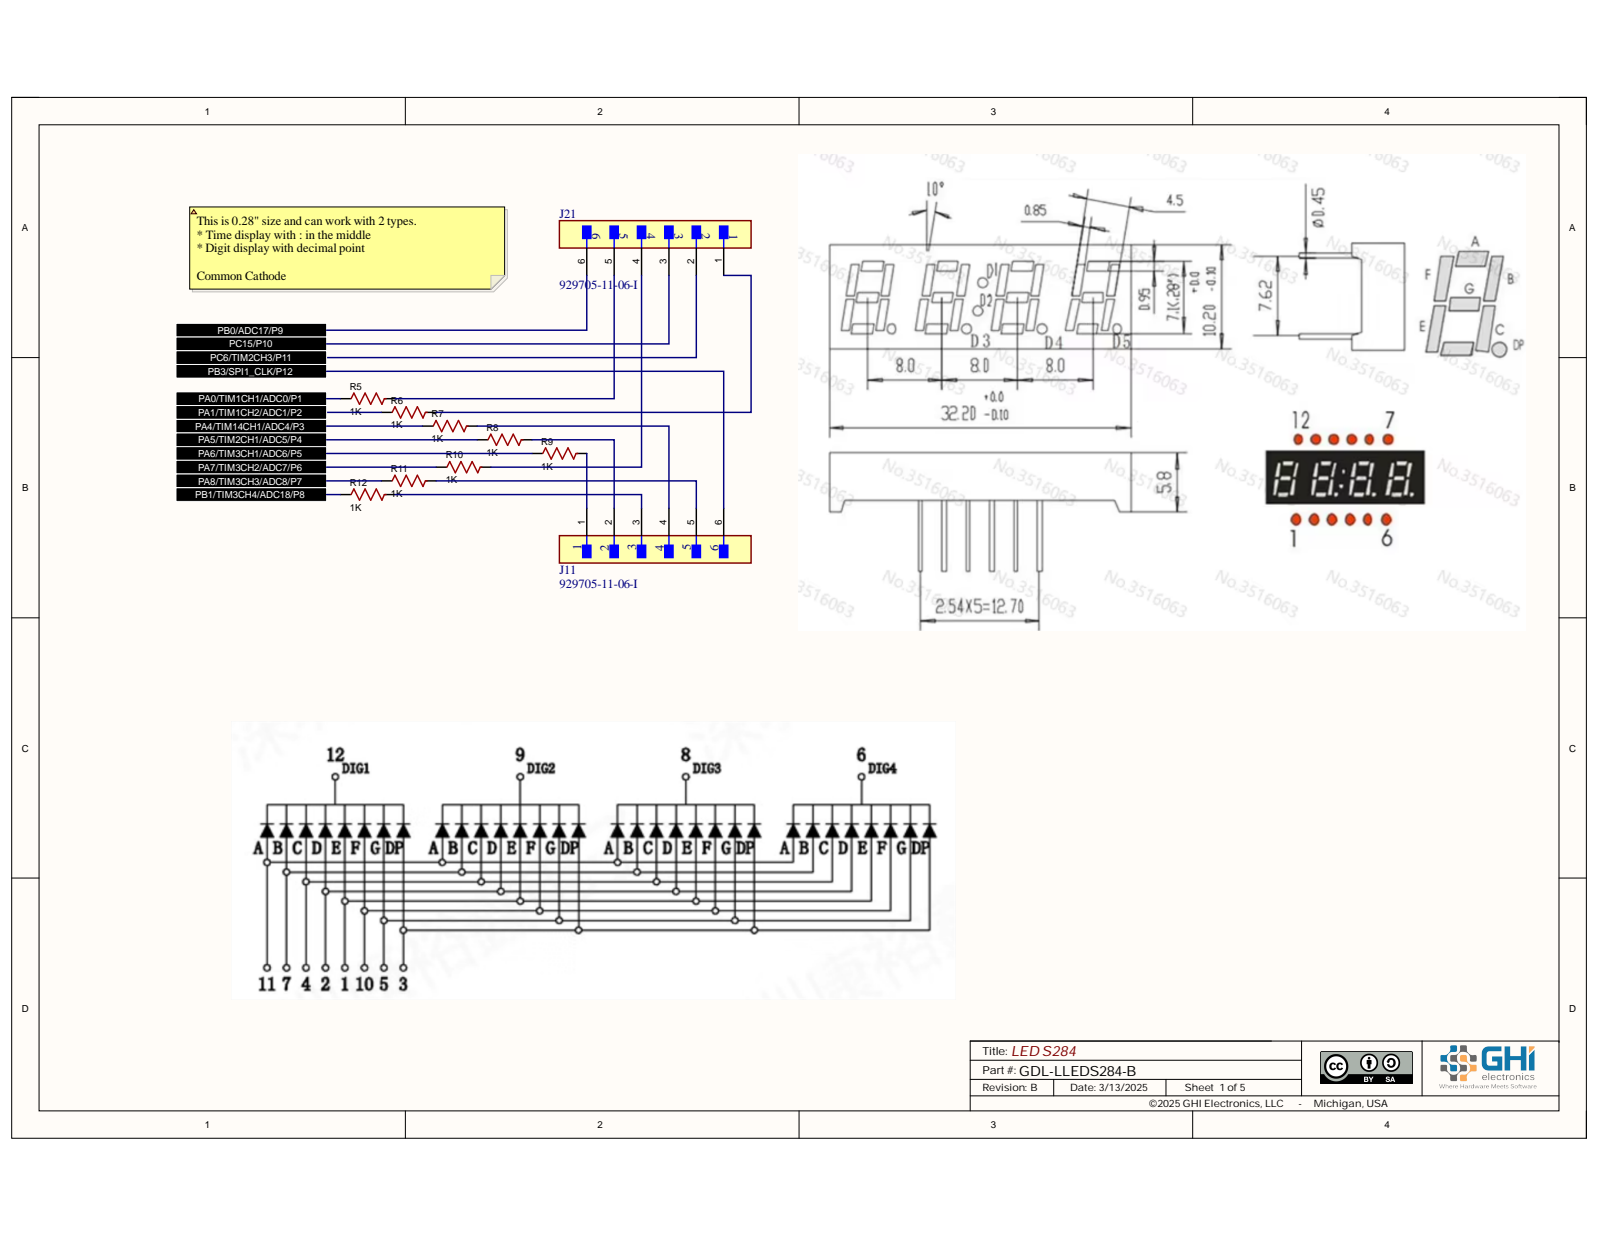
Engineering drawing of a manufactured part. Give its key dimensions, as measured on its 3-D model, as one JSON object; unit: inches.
{"part_name": "PCB; Board; STAT1; 0603 LED Green (+5 more)", "step_written_by": "Open CASCADE 7.5 (AUTOMOTIVE_DESIGN)", "units": "inches", "bodies": {"solids": 131, "faces": 3481, "planar": 1844, "cylindrical": 894, "other": 743}, "overall_size": [1.85, 0.67, 0.669], "volume_in3": 0.256, "surface_area_in2": 7.068, "round_holes": [[0.04, 12], [0.118, 4], [0.04, 2]], "round_bosses_or_shafts": [[0.024, 2]], "partial_cylinders_radius": [[0.005, 35], [0.006, 14], [0.138, 4], [0.007, 2], [0.007, 2], [0.007, 2]], "face_to_face_distances": [0.063, 0.181, 0.496, 0.118, 0.433, 0.315, 0.402, 0.3, 0.025, 0.1], "hole_center_spacings": [0.3, 0.1, 0.316, 0.2, 0.361, 0.424, 0.5, 0.4]}
